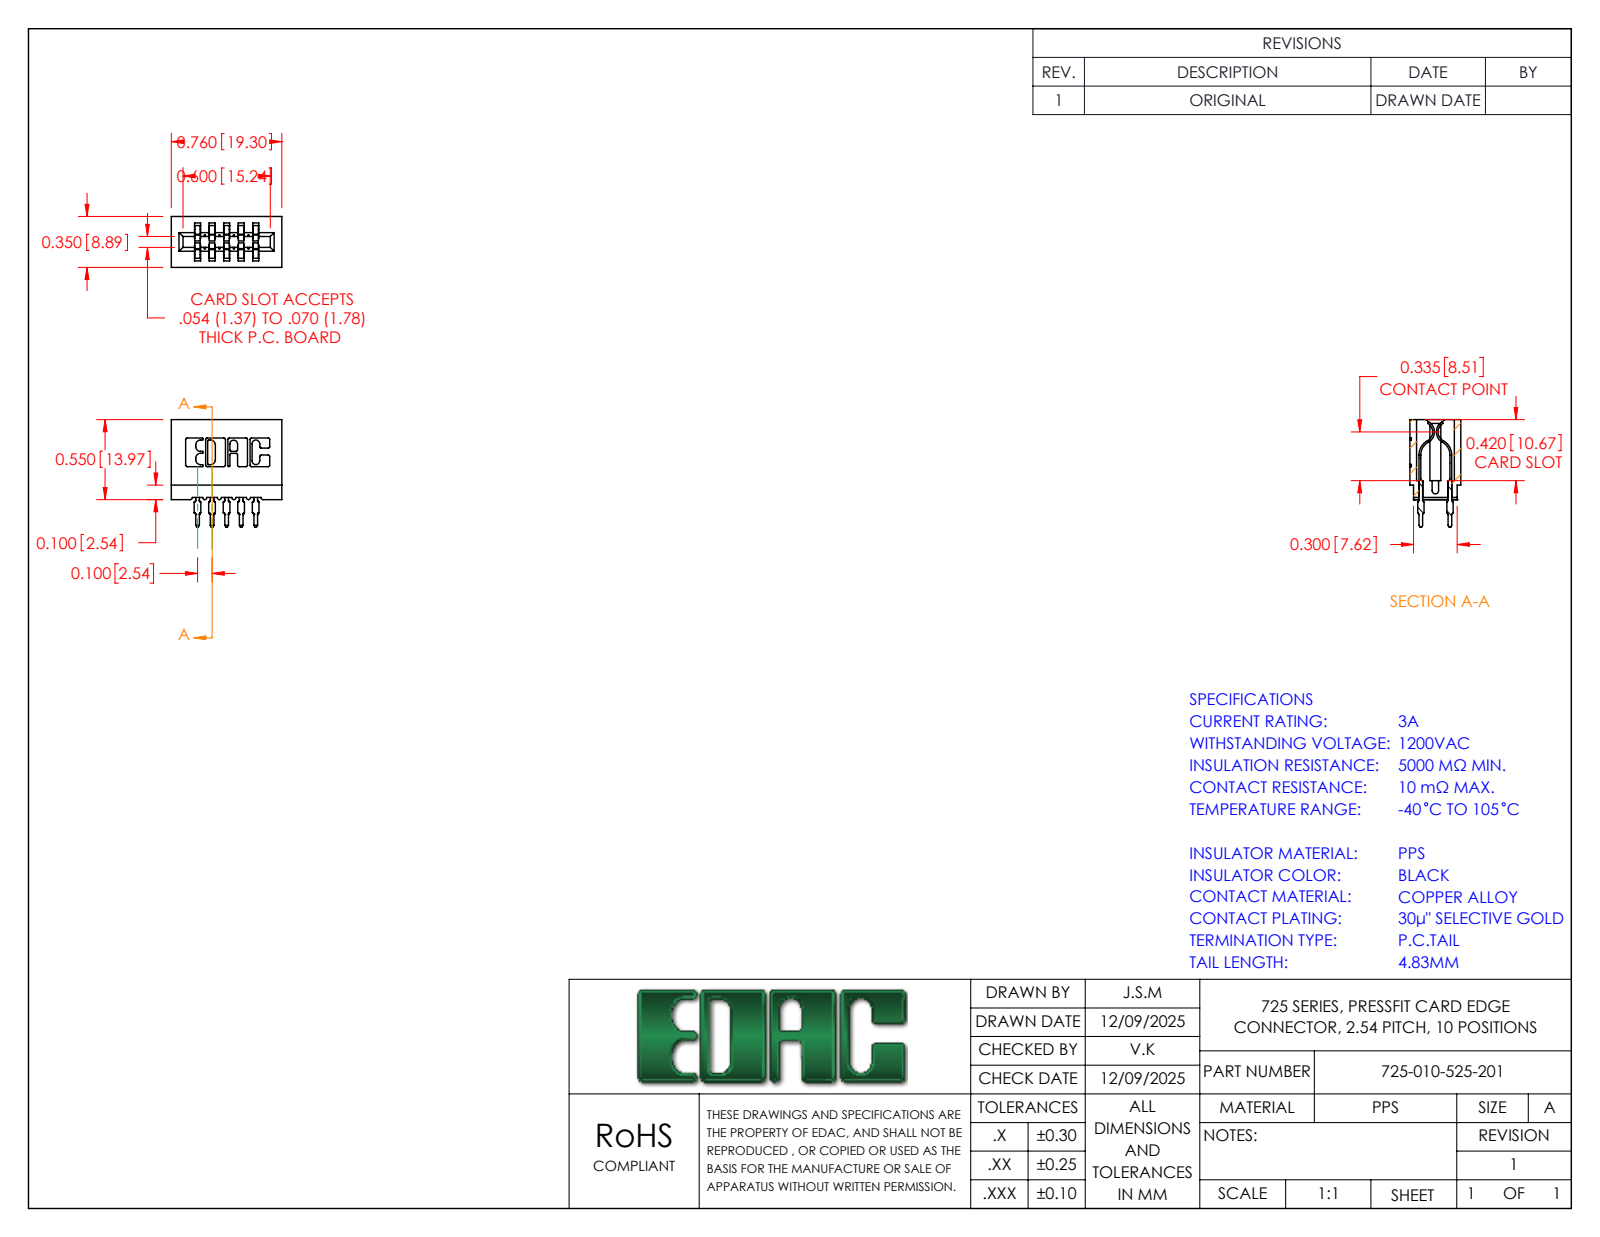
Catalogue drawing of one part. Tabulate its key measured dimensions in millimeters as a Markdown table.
| quantity | value |
| --- | --- |
| part name | 725 Part_Insulator Option - 01; 745-292-001_525; 725-010-525-201 |
| STEP written by | SolidWorks 2023 (CONFIG_CONTROL_DESIGN) |
| units | millimeters |
| bodies | 11 solids, 990 faces (515 planar, 215 cylindrical, 260 other) |
| overall size | 19.3 × 18.8 × 8.89 |
| volume | 1 714 mm³ |
| surface area | 2 824 mm² |
| partial cylindrical surfaces (radius × count) | 0.25 × 22, 0.55 × 20, 0.38 × 10, 0.13 × 8, 0.28 × 8, 0.17 × 6, 0.8 × 6, 0.67 × 3 |
| main face-to-face distances | 2.54, 5.08, 1.07, 7.62, 3.61, 1.47, 6.15, 4.01, 5.38, 8.89 |
